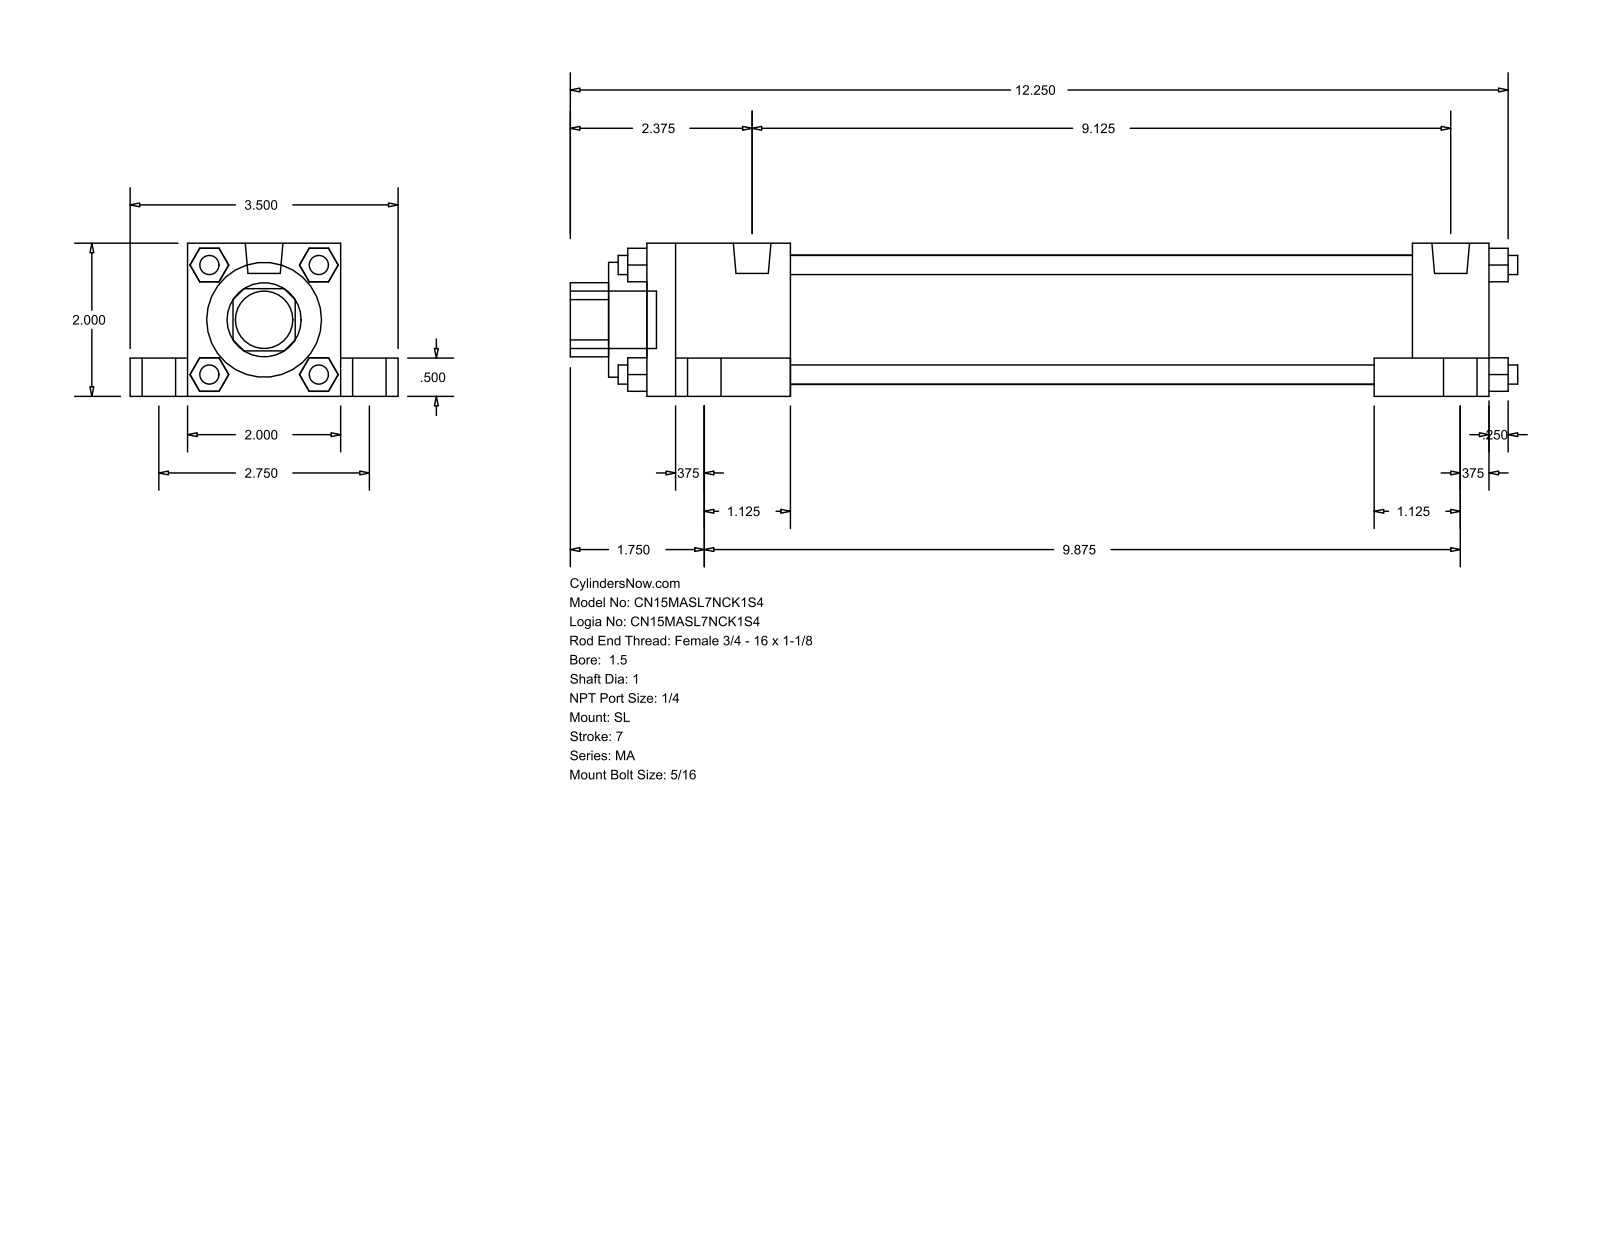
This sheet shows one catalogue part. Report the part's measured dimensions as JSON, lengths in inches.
{"part_name": "MA_SL__0150_1", "step_written_by": "GSSL Pune (CONFIG_CONTROL_DESIGN)", "units": "inches", "bodies": {"solids": 0, "faces": 148, "planar": 112, "cylindrical": 36, "other": 0}, "overall_size": [12.375, 3.5, 2], "round_holes": [[1, 1], [1.5, 1], [1.69, 1]], "round_bosses_or_shafts": [[0.687, 4], [0.437, 4], [0.313, 4], [0.25, 4], [0.492, 2], [0.75, 1]], "partial_cylinders_radius": [[0.484, 1]], "face_to_face_distances": [2, 0.5, 0.75, 0.375, 2.75, 1.5, 0.25, 11, 1, 10]}
